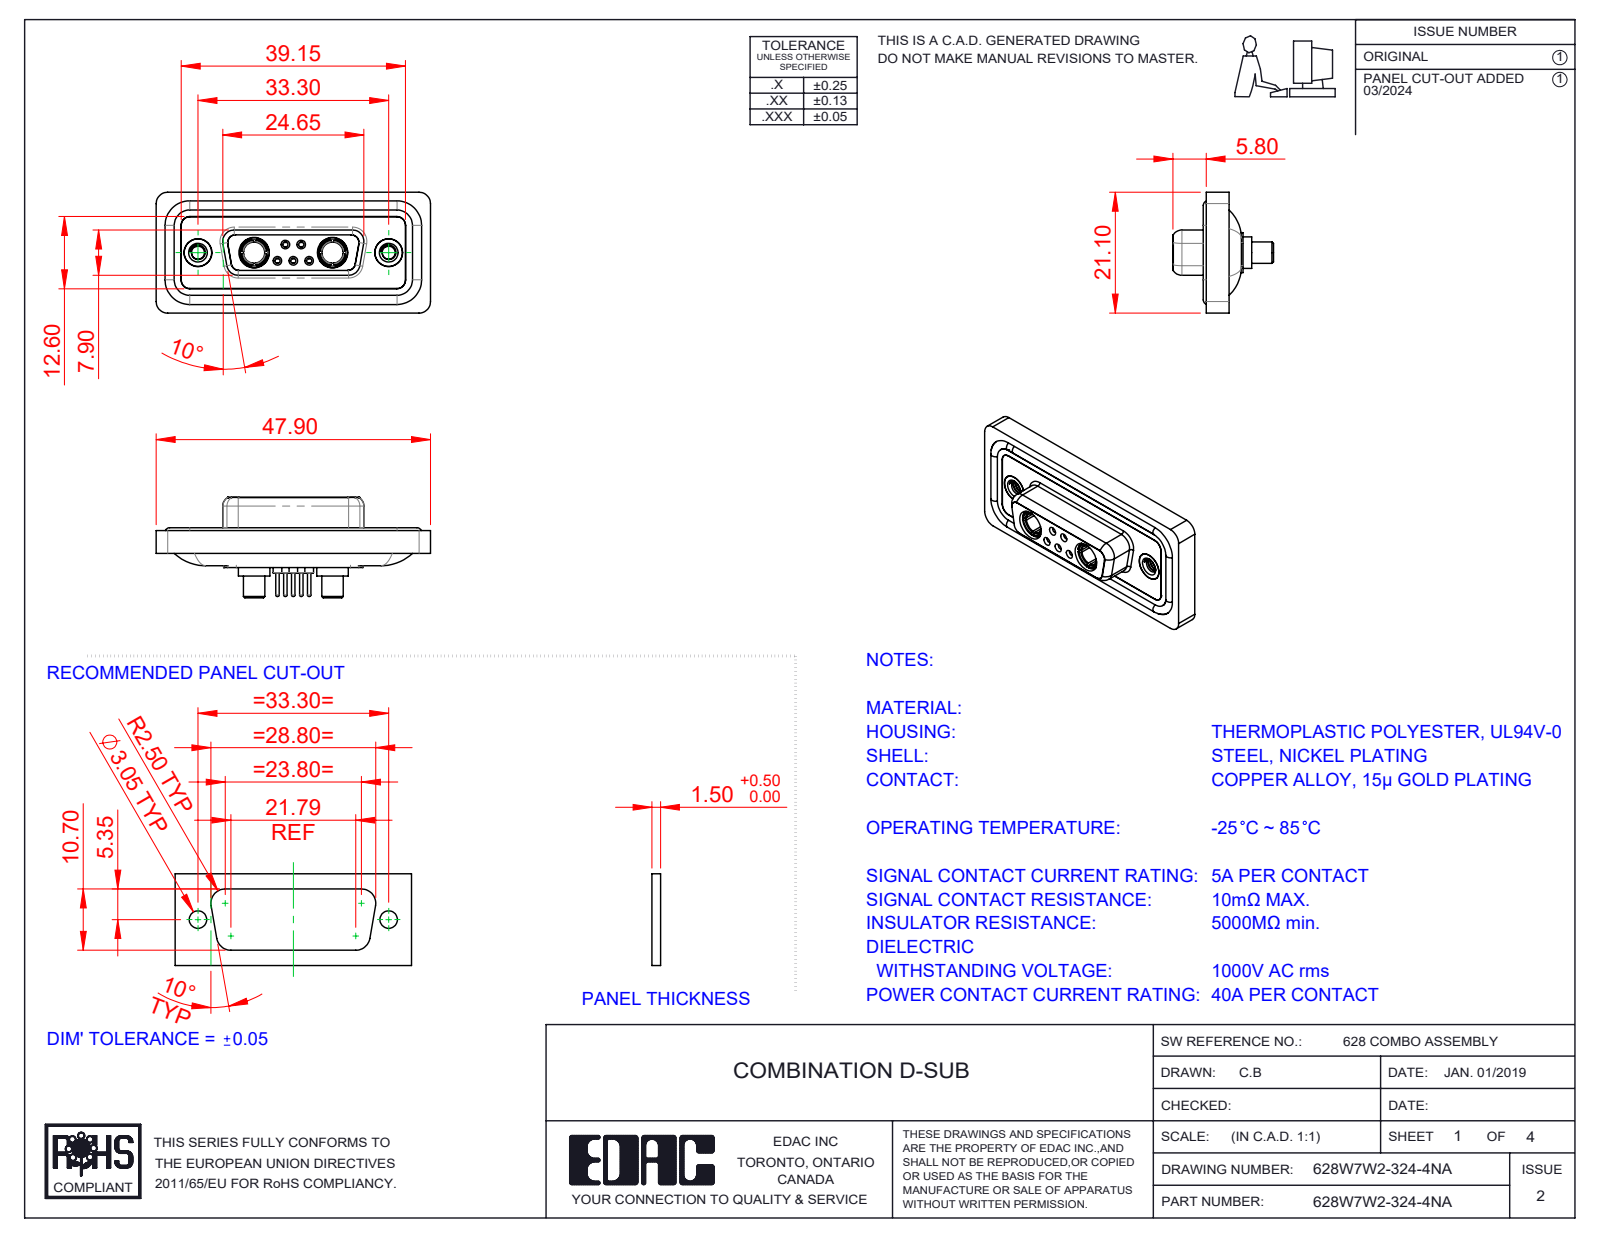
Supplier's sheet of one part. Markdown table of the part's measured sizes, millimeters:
| quantity | value |
| --- | --- |
| part name | 628Combo Threaded Rivet_A; 628Combo Shell Front_15 Contacts; Power Socket_40A S; 628Combo Housing_7W2 (+5 more) |
| STEP written by | SolidWorks 2023 (CONFIG_CONTROL_DESIGN) |
| units | millimeters |
| bodies | 16 solids, 807 faces (238 planar, 331 cylindrical, 238 other) |
| overall size | 47.9 × 21.1 × 17.55 |
| volume | 6 116 mm³ |
| surface area | 9 904 mm² |
| round holes (diameter × count) | 0.9 × 5, 1.1 × 5, 1.5 × 5, 2 × 5, 4.85 × 4, 1.6 × 3, 1.7 × 2, 2.26 × 2, 3.7 × 2, 4 × 2, 4.05 × 2, 5 × 2 |
| round bosses / shafts (diameter × count) | 1.6 × 6, 2.2 × 5, 0.6 × 5, 5.5 × 2, 5.2 × 2, 4.96 × 2, 4.95 × 2, 4.8 × 2 |
| partial cylindrical surfaces (radius × count) | 1.5 × 22, 2 × 20, 1.35 × 12, 1.6 × 8, 0.25 × 4, 0.5 × 4, 0.6 × 4, 0.65 × 4 |
| main face-to-face distances | 0.4, 1.8, 1.6, 0.5, 2.9, 7.45, 1.1, 5.65, 6.6, 7.05 |
| hole center spacings | 3.16, 2.77, 9.8, 23.5, 4.31, 4.33, 5.03, 5.04 |
